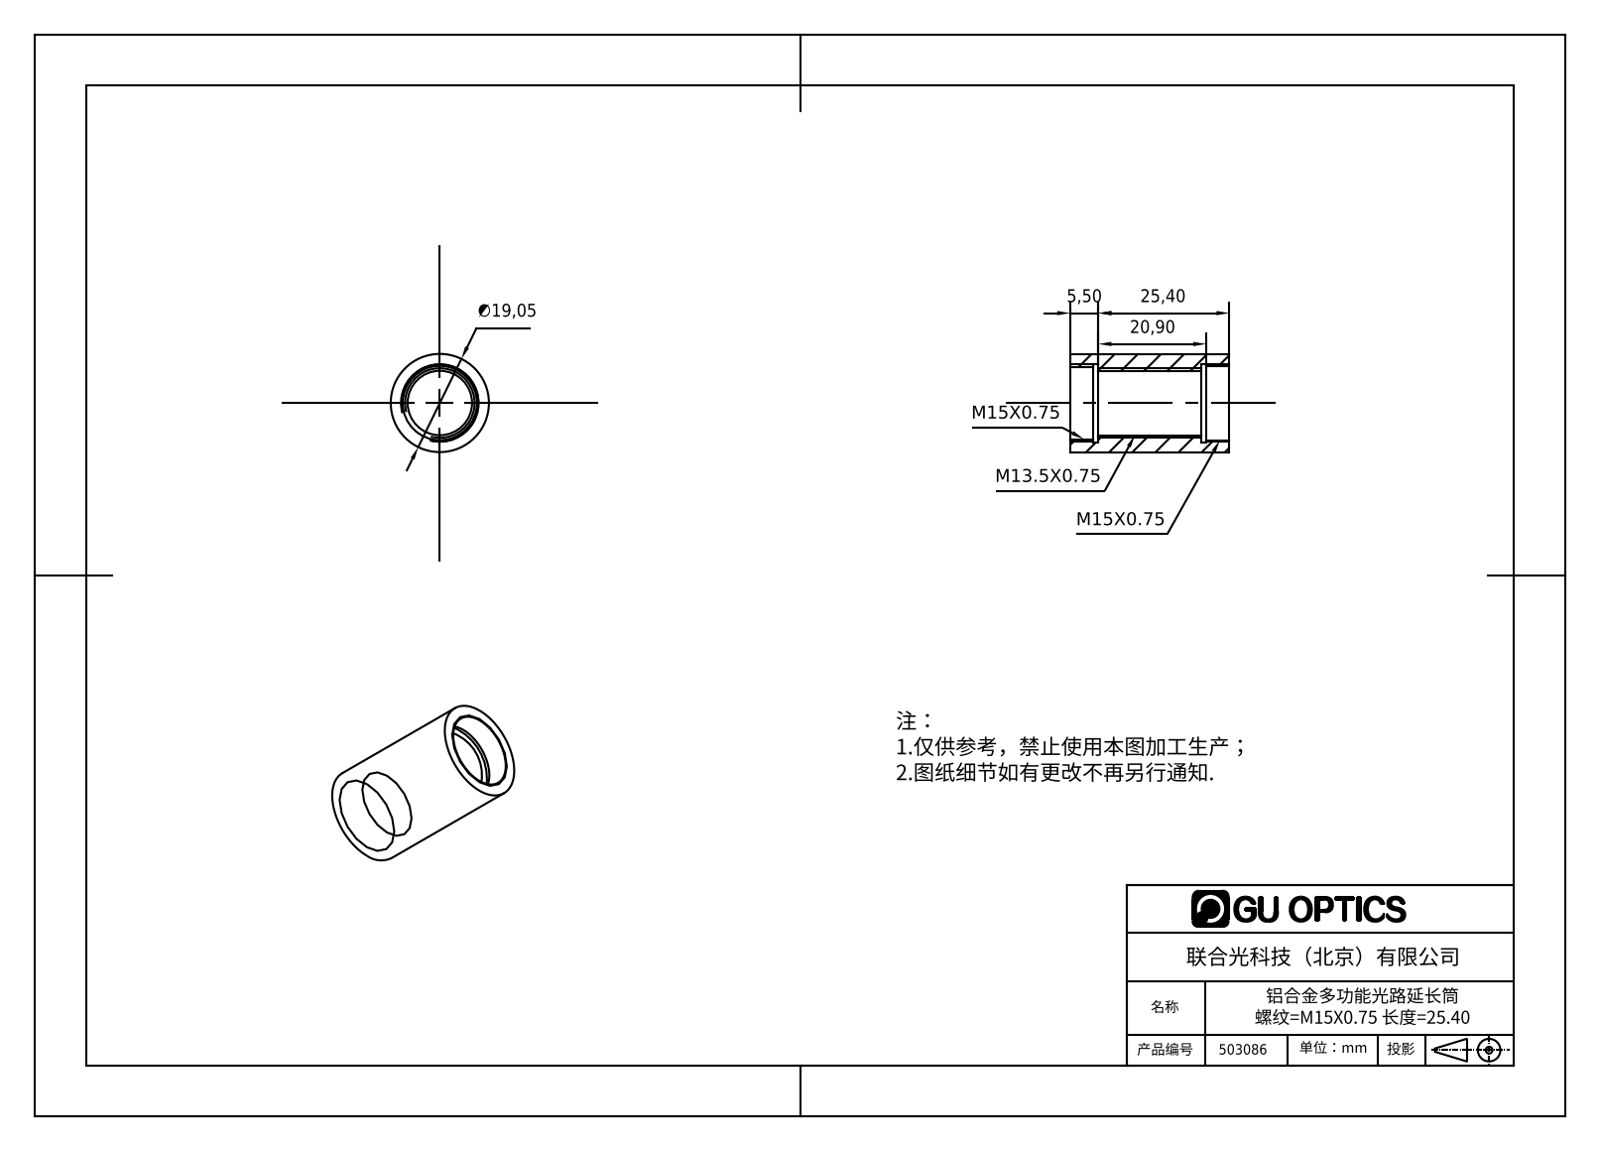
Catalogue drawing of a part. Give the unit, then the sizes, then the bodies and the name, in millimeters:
Units: millimetres
Overall size (bounding box): 30.9 × 19.05 × 19.05
Round holes (diameter × count): ⌀12.5 ×1, ⌀14 ×1, ⌀14.4 ×1, ⌀15.2 ×1
Round bosses / shafts (diameter × count): ⌀19.05 ×1
Main face-to-face distances: 30.9, 5.5, 25.4, 19.9, 4.5, 26.4, 1, 20.9, 21.9
Volume: 4 577 mm³ · Surface area: 3 545 mm²
Bodies: 1 solid, 18 faces (6 planar, 12 cylindrical, 0 other)
Part name (STEP PRODUCT): 503086
STEP written by: SolidWorks 2016 (AUTOMOTIVE_DESIGN)
